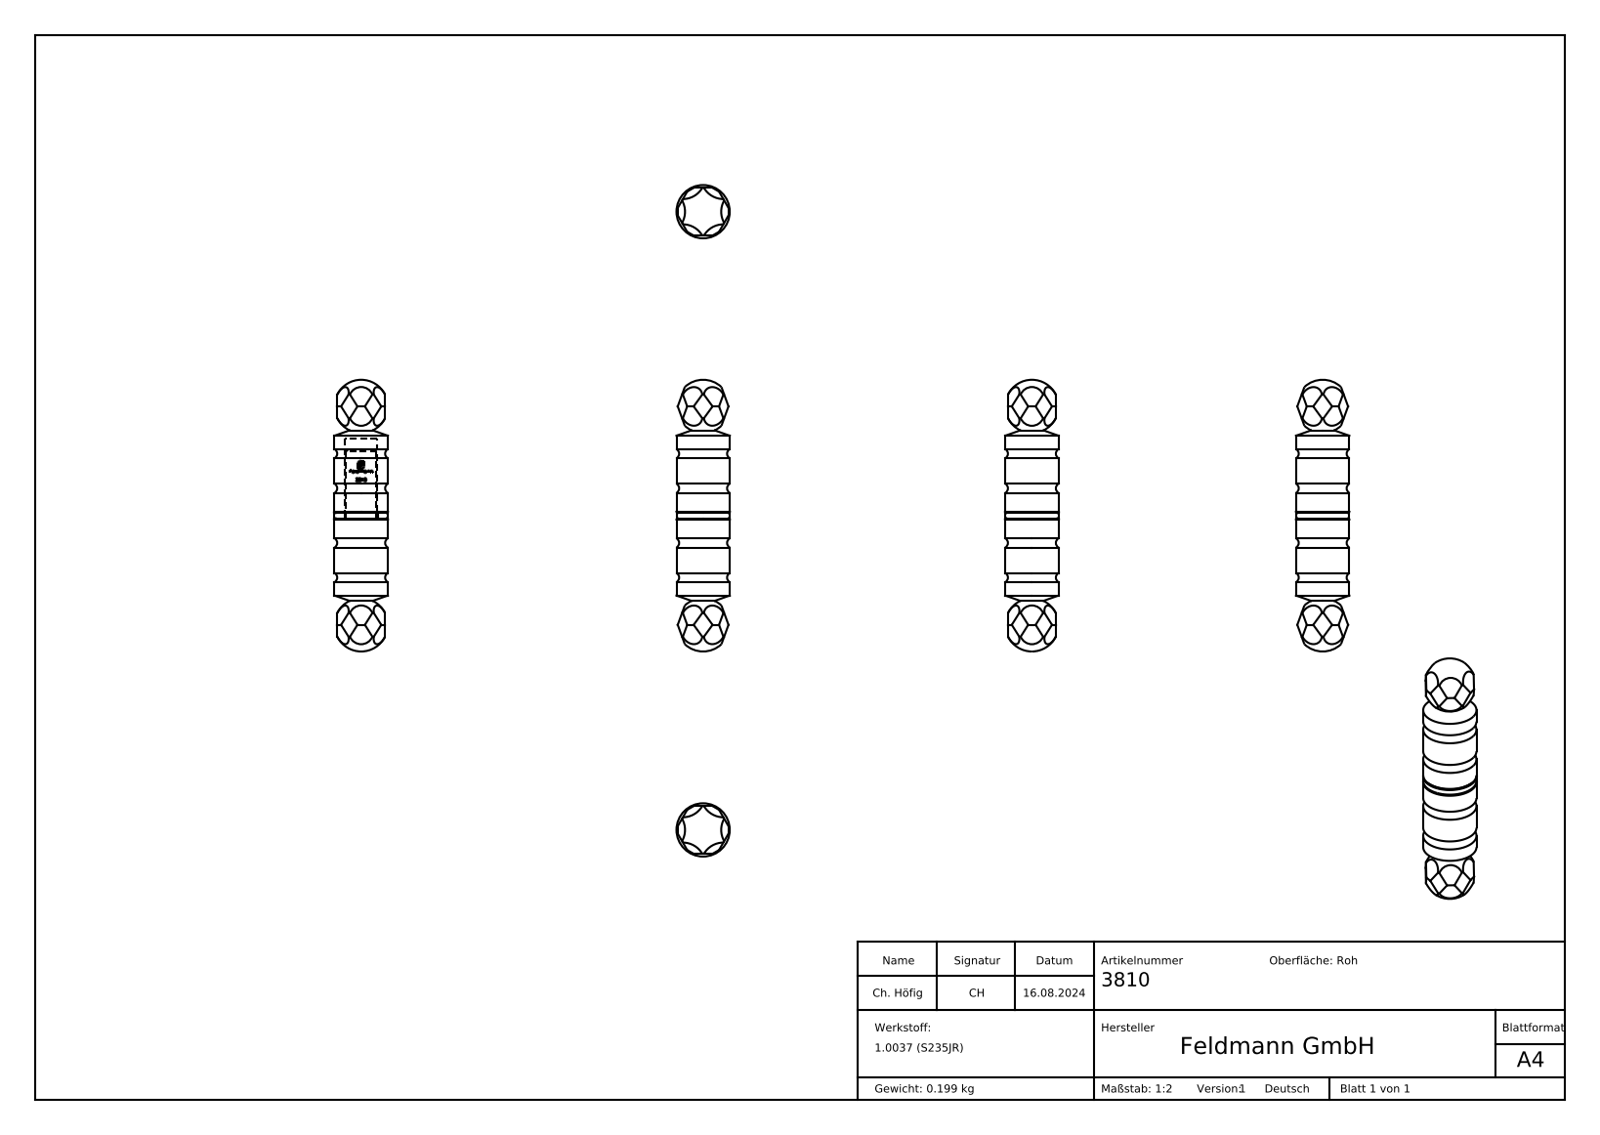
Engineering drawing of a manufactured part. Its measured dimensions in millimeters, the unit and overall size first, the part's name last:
Units: millimetres
Overall size (bounding box): 102 × 20 × 20
Round holes (diameter × count): ⌀12 ×1, ⌀12.5 ×1
Round bosses / shafts (diameter × count): ⌀20 ×1, ⌀11.5 ×1
Partial cylindrical surfaces — rounded edges, fillets, slot ends (radius × count): R6.1 ×1
Main face-to-face distances: 17.9, 28.04, 2, 10.14, 45.94, 30, 28, 26, 24, 4
Volume: 25 483 mm³ · Surface area: 9 684 mm²
Bodies: 3 solids, 278 faces (127 planar, 29 cylindrical, 122 other)
Part name (STEP PRODUCT): 3810 - 3811 - 3812 Teil1-3_3810 Teil1; 3810 - 3811 - 3812 Teil1-3_3810 Teil3; 3810 - 3811 - 3812 Teil1-3_3810 Teil2; 3810
STEP written by: SolidWorks 2018 (CONFIG_CONTROL_DESIGN)
